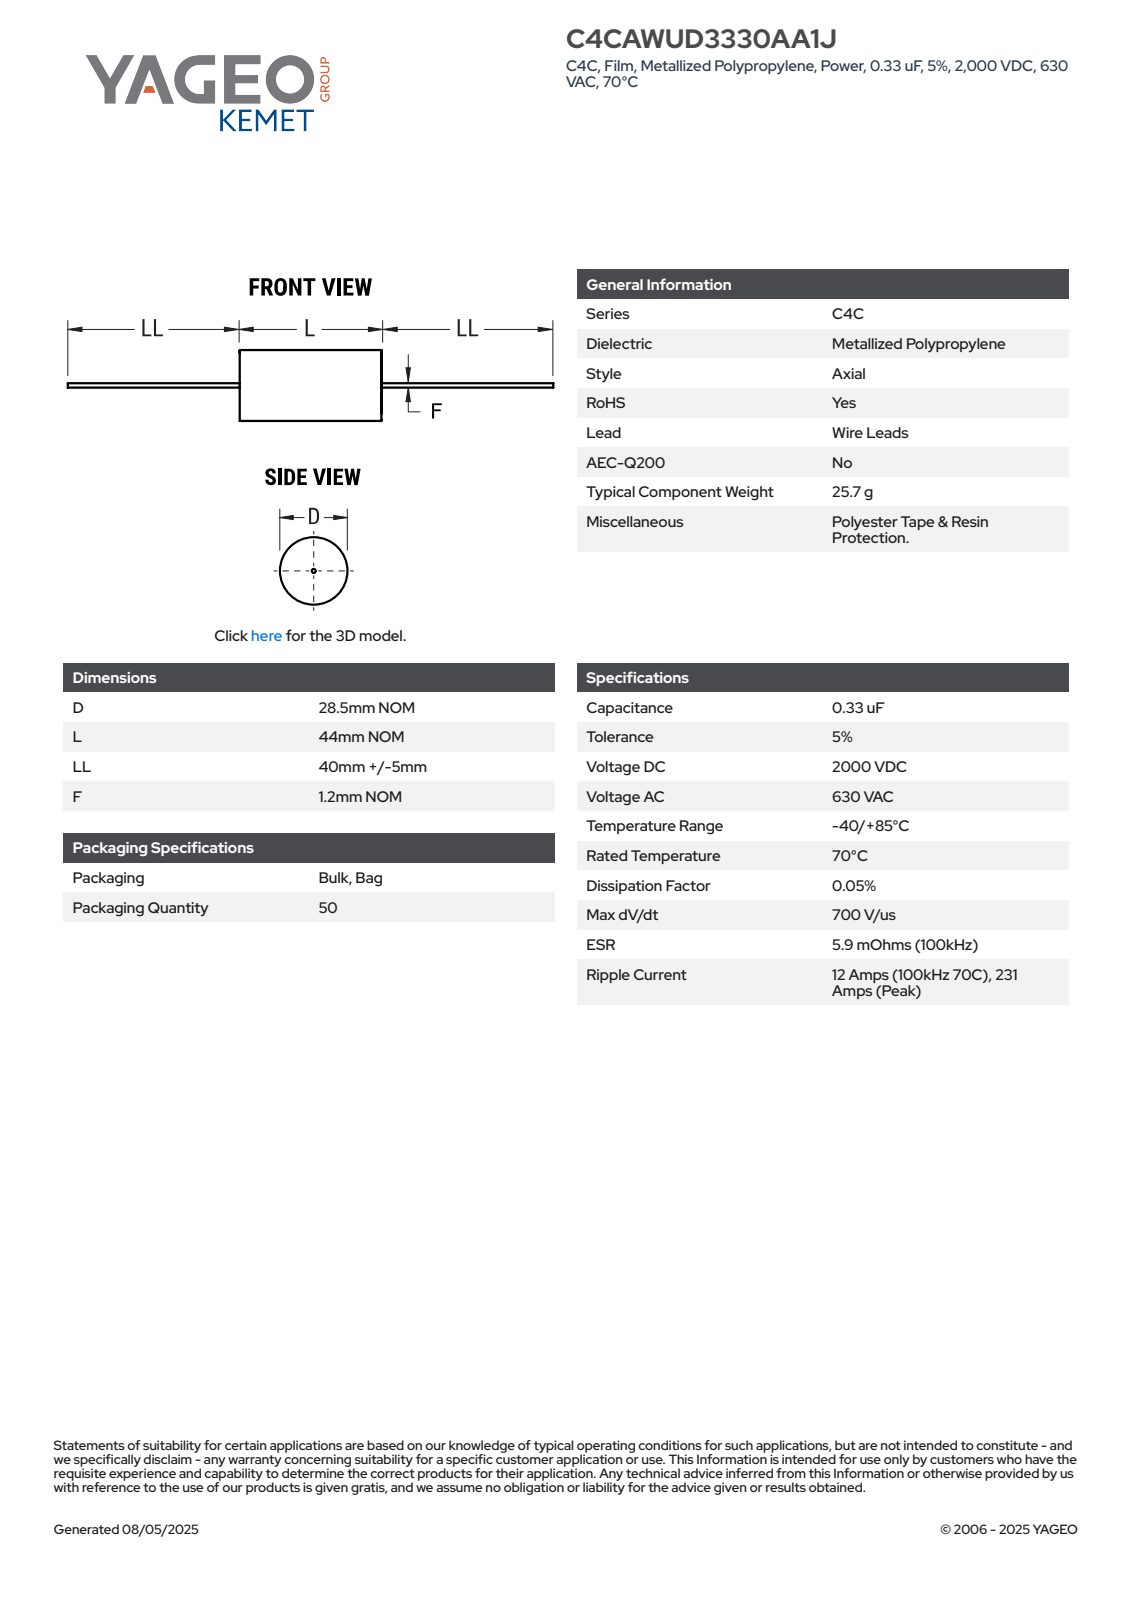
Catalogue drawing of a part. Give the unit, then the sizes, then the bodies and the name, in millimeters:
Units: millimetres
Overall size (bounding box): 134 × 28.5 × 28.5
Round bosses / shafts (diameter × count): ⌀28.5 ×1, ⌀1.2 ×1
Partial cylindrical surfaces — rounded edges, fillets, slot ends (radius × count): R14.24 ×1
Main face-to-face distances: 44, 43.99, 44.99, 45, 88.99, 134, 89.01, 89, 45.01
Volume: 28 171 mm³ · Surface area: 6 829 mm²
Bodies: 2 solids, 87 faces (28 planar, 28 cylindrical, 31 other)
Part name (STEP PRODUCT): CFP_ACWF_28.5X44_D28.5L44LL45F1.2
STEP written by: SolidWorks 2014 (AUTOMOTIVE_DESIGN)
